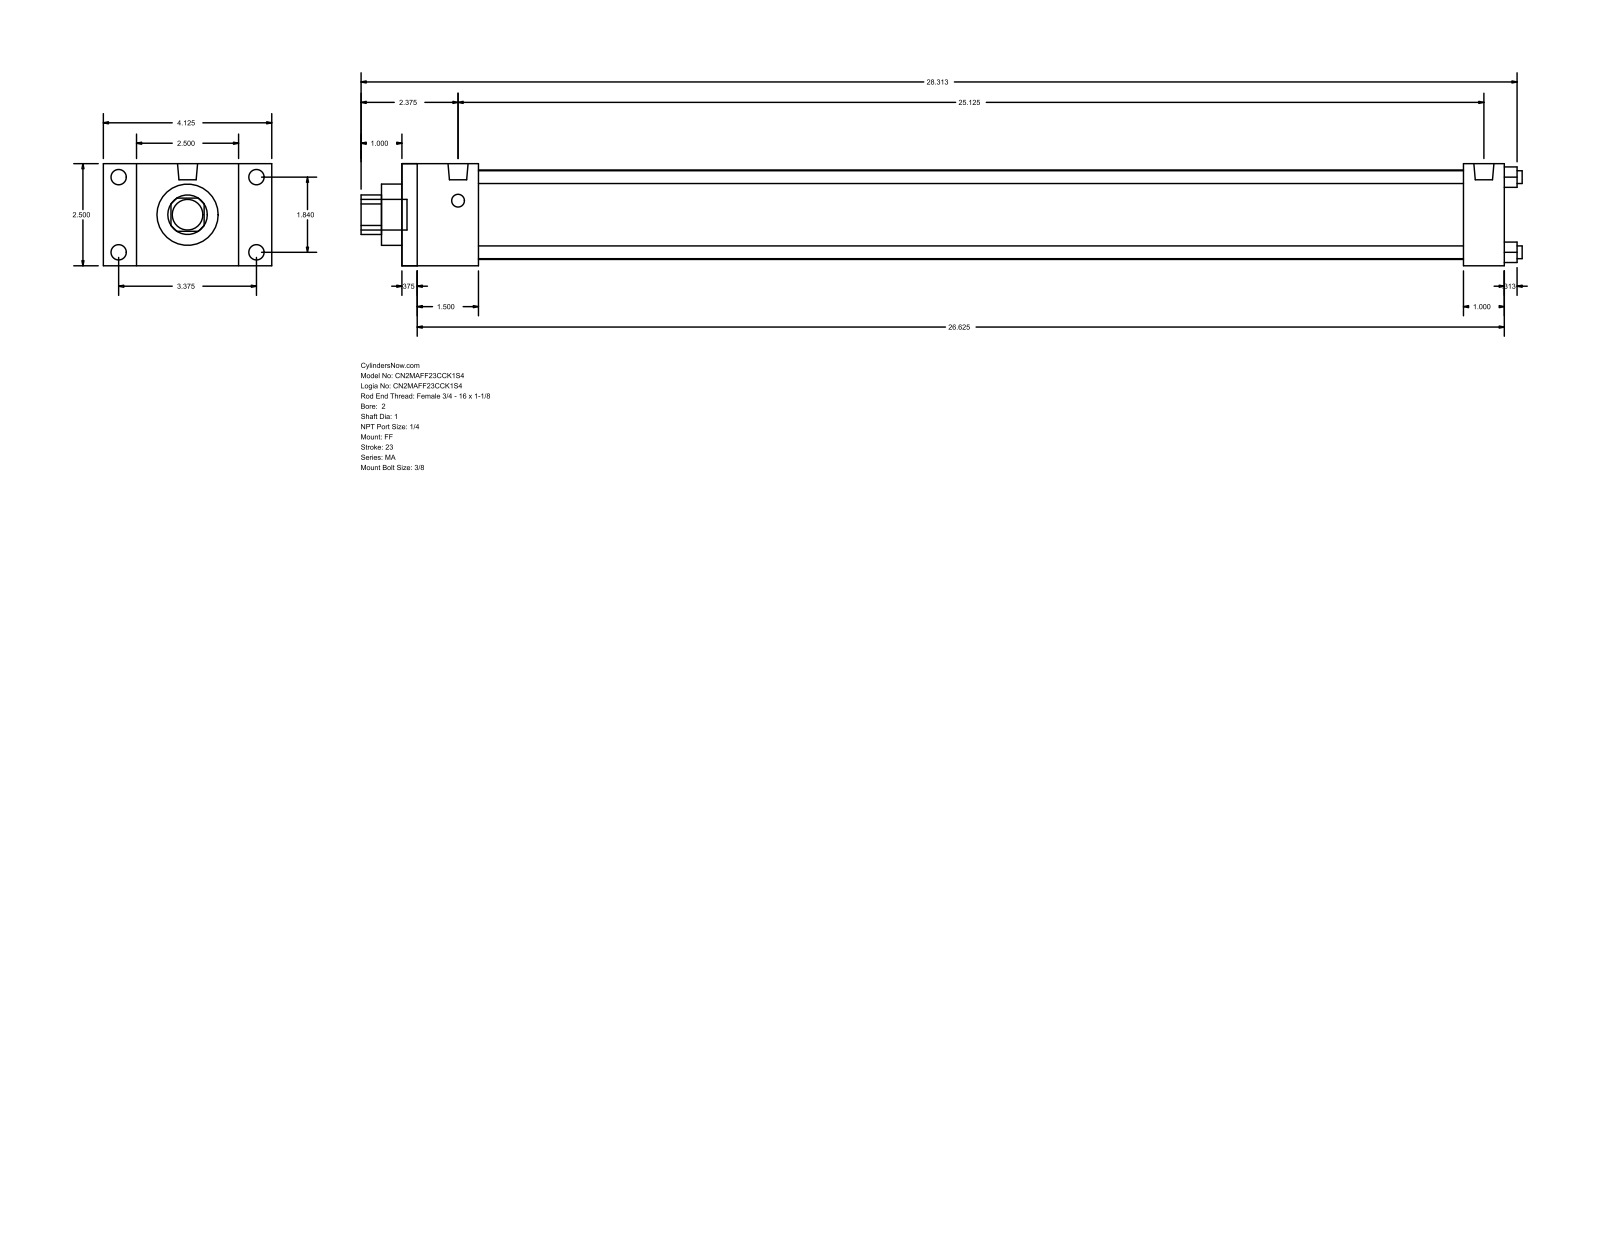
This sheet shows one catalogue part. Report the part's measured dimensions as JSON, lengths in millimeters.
{"part_name": "MA_FF__0200_1", "step_written_by": "GSSL Pune (CONFIG_CONTROL_DESIGN)", "units": "millimeters", "bodies": {"solids": 0, "faces": 92, "planar": 64, "cylindrical": 28, "other": 0}, "overall_size": [722.31, 104.78, 63.5], "round_holes": [[7.94, 4], [25.4, 1], [38.1, 1], [55.63, 1]], "round_bosses_or_shafts": [[9.53, 4], [7.94, 4], [12.49, 2], [19.05, 1]], "partial_cylinders_radius": [[12.29, 1]], "face_to_face_distances": [63.5, 685.8, 9.52, 676.28, 25.4, 20.64, 12.7, 47.63, 660.4, 38.11], "hole_center_spacings": [33.05, 46.74, 66.1]}
